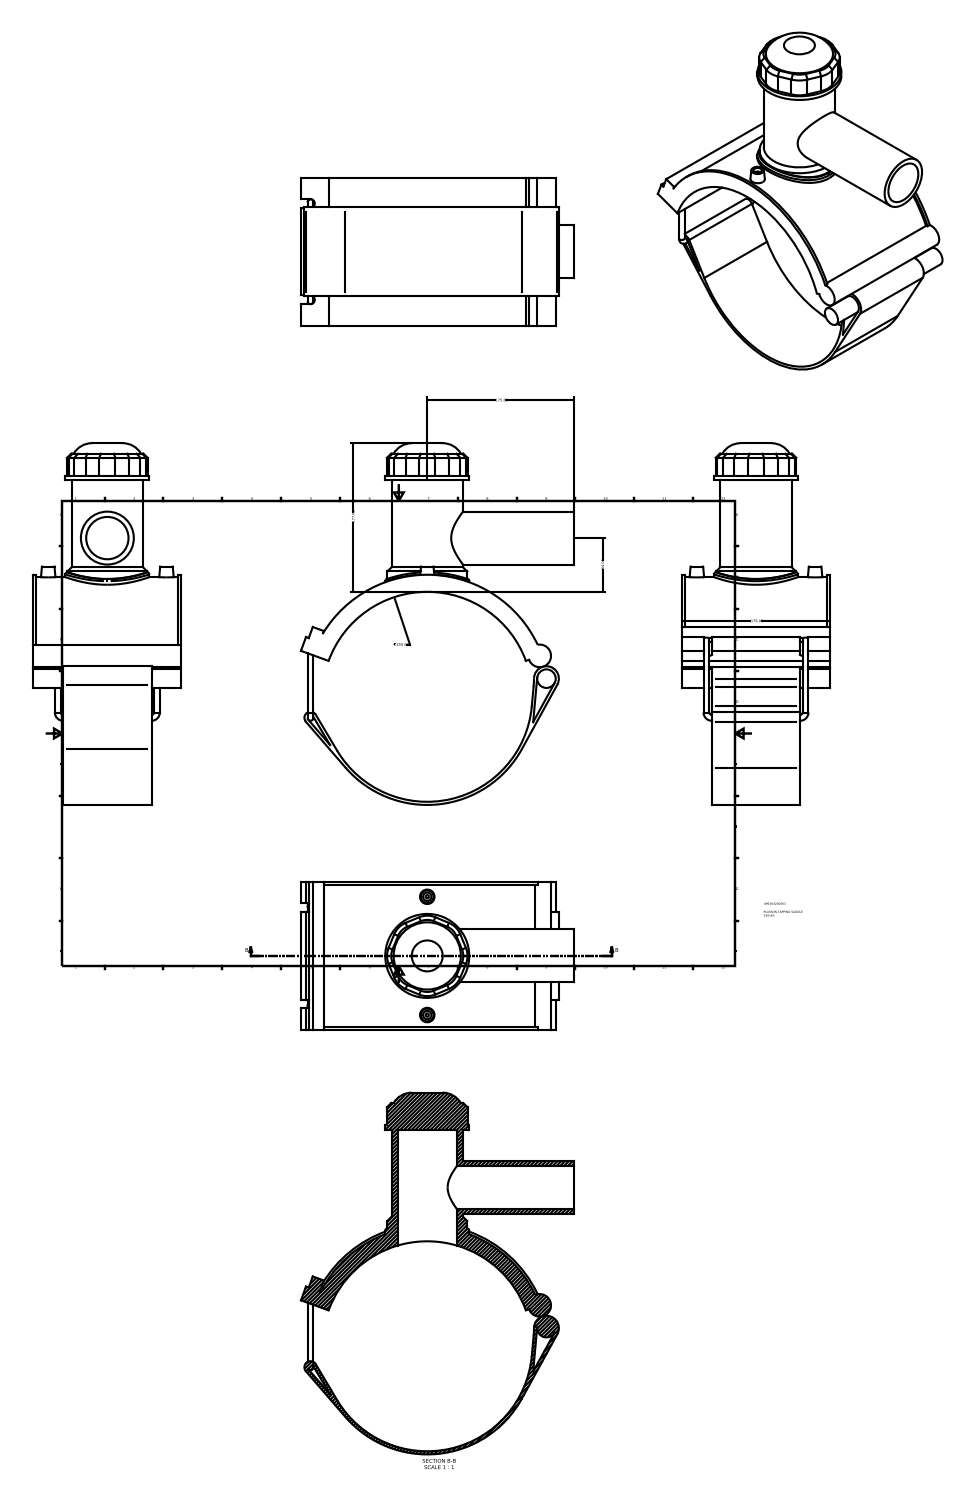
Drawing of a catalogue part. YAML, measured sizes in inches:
part_name: "496304250063"
step_written_by: "Autodesk Inventor 2015 (CONFIG_CONTROL_DESIGN)"
units: inches
bodies: {solids: 1, faces: 121, planar: 68, cylindrical: 38, other: 15}
overall_size: [16.959, 12.809, 6.929]
volume: 125.8
surface_area: 637.5
round_holes:
  - {diameter: 0.394, count: 2}
  - {diameter: 1.984, count: 1}
  - {diameter: 2.756, count: 1}
round_bosses_or_shafts:
  - {diameter: 0.276, count: 2}
  - {diameter: 0.157, count: 2}
  - {diameter: 3.937, count: 1}
  - {diameter: 3.74, count: 1}
  - {diameter: 3.346, count: 1}
  - {diameter: 2.48, count: 1}
  - {diameter: 0.871, count: 1}
partial_cylinders:
  - {radius: 0.984, count: 8}
  - {radius: 0.207, count: 2}
  - {radius: 4.921, count: 2}
  - {radius: 0.138, count: 1}
  - {radius: 0.285, count: 1}
  - {radius: 0.53, count: 1}
  - {radius: 0.583, count: 1}
  - {radius: 5.069, count: 1}
face_to_face_distances: [0.148, 6.929, 0.149, 1.386, 5.543, 0.689, 0.551, 0.131, 1.241, 0.138]
hole_center_spacings: [2.772, 5.543]
